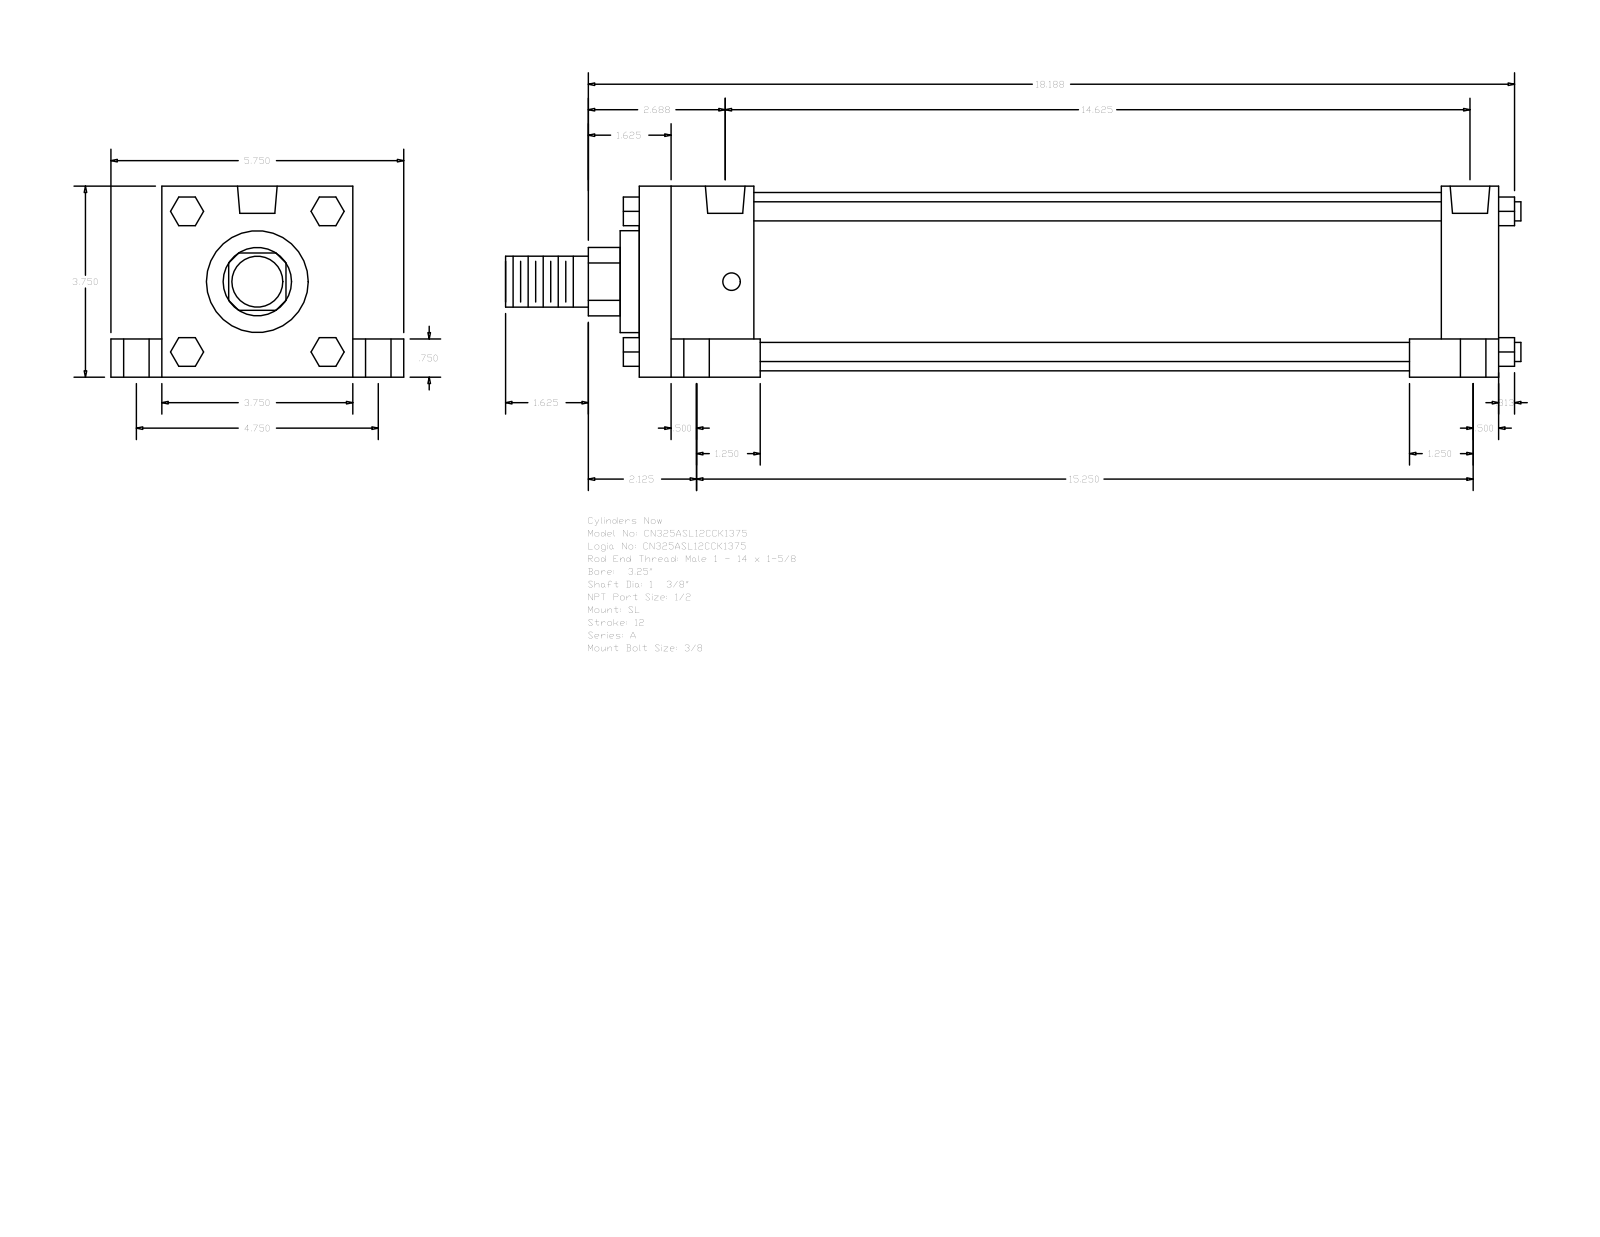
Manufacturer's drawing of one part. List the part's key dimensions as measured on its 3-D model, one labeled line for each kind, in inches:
Part name (STEP PRODUCT): A_SL__0325_1.375
STEP written by: GSSL Pune (CONFIG_CONTROL_DESIGN)
Units: inches
Bodies: 0 solids, 150 faces (114 planar, 36 cylindrical, 0 other)
Overall size (bounding box): 19.937 × 5.75 × 3.75
Round holes (diameter × count): ⌀0.344 ×4, ⌀0.5 ×4, ⌀0.75 ×4, ⌀0.778 ×2
Round bosses / shafts (diameter × count): ⌀0.375 ×4, ⌀3.5 ×1, ⌀2 ×1, ⌀1.375 ×1, ⌀1 ×1
Partial cylindrical surfaces — rounded edges, fillets, slot ends (radius × count): R0.672 ×1
Main face-to-face distances: 3.75, 16.875, 1, 4.75, 0.75, 3, 2.25, 1.125, 15.75, 13.5
Hole centre spacings: 0.125, 2.376, 2.383, 2.441, 2.473, 4.75, 14.375, 14.5
